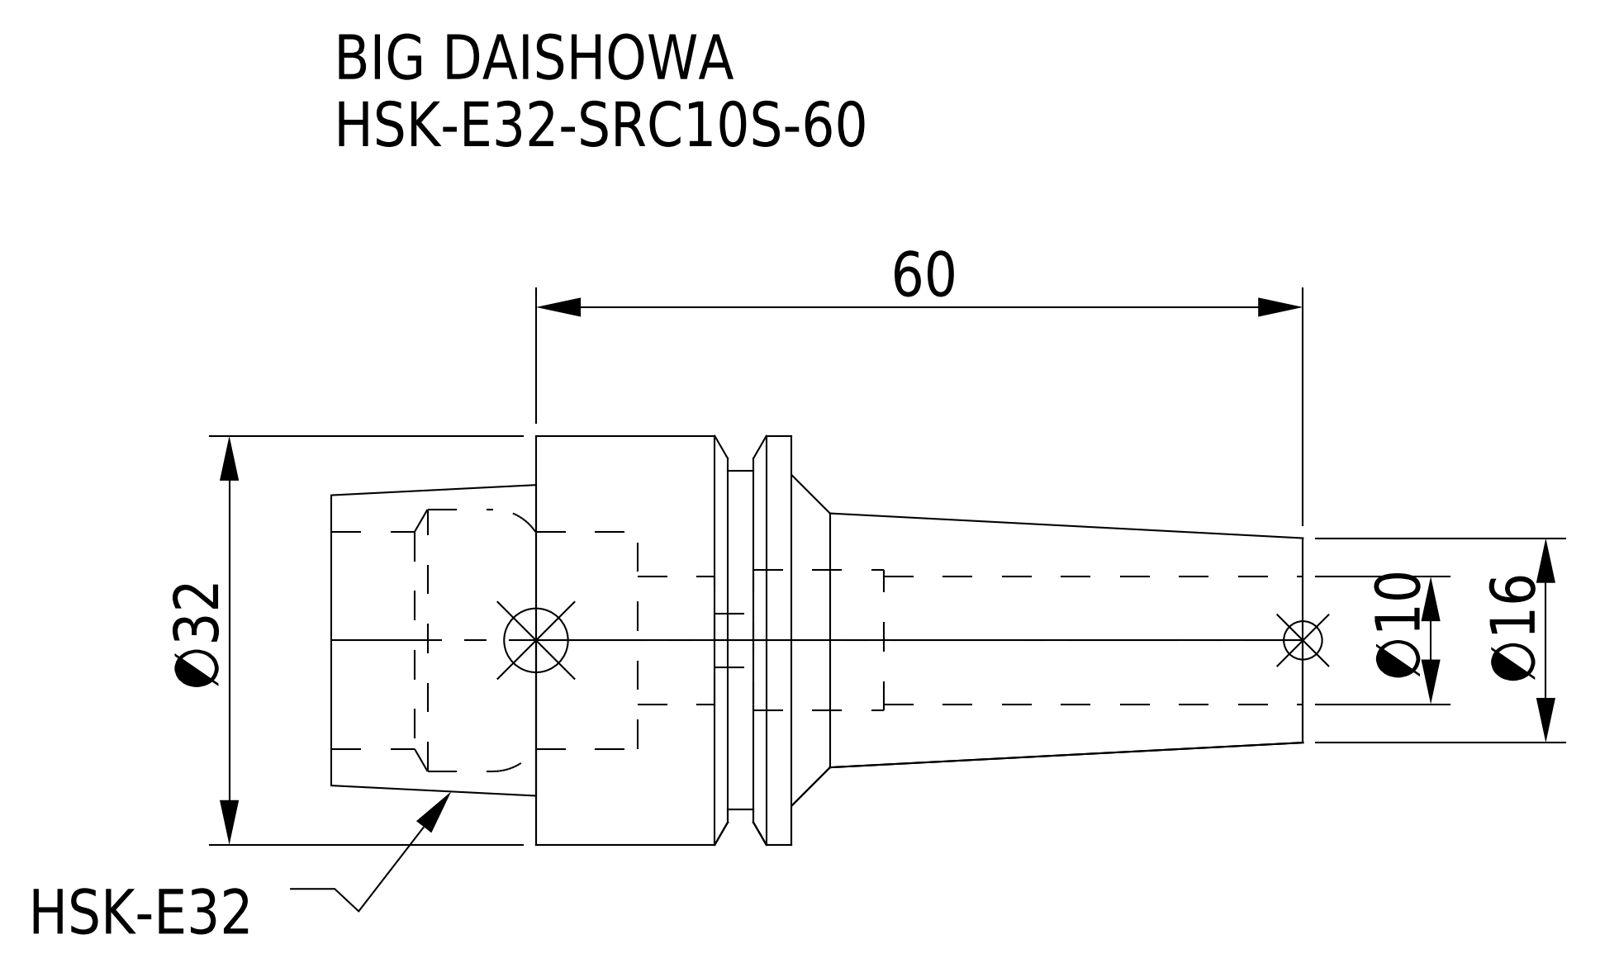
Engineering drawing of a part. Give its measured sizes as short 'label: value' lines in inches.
name: HSK-E32-SRC10S-60
written by: CREO PARAMETRIC BY PTC INC, 2016380 (AUTOMOTIVE_DESIGN)
unit: in
bodies: 1 solid, 46 faces (10 planar, 22 cylindrical, 14 other)
size: 2.992 × 1.26 × 1.26
volume: 1.384 in³; area: 15.82 in²
holes: 1× ⌀0.165, 1× ⌀0.394, 1× ⌀0.433, 1× ⌀0.669, 1× ⌀0.807
bosses: 1× ⌀1.26, 1× ⌀1.043
face distances: 0.787, 1.417, 0.63, 0.118, 0.669, 1.299, 0.474, 0.356, 0.313, 0.943
